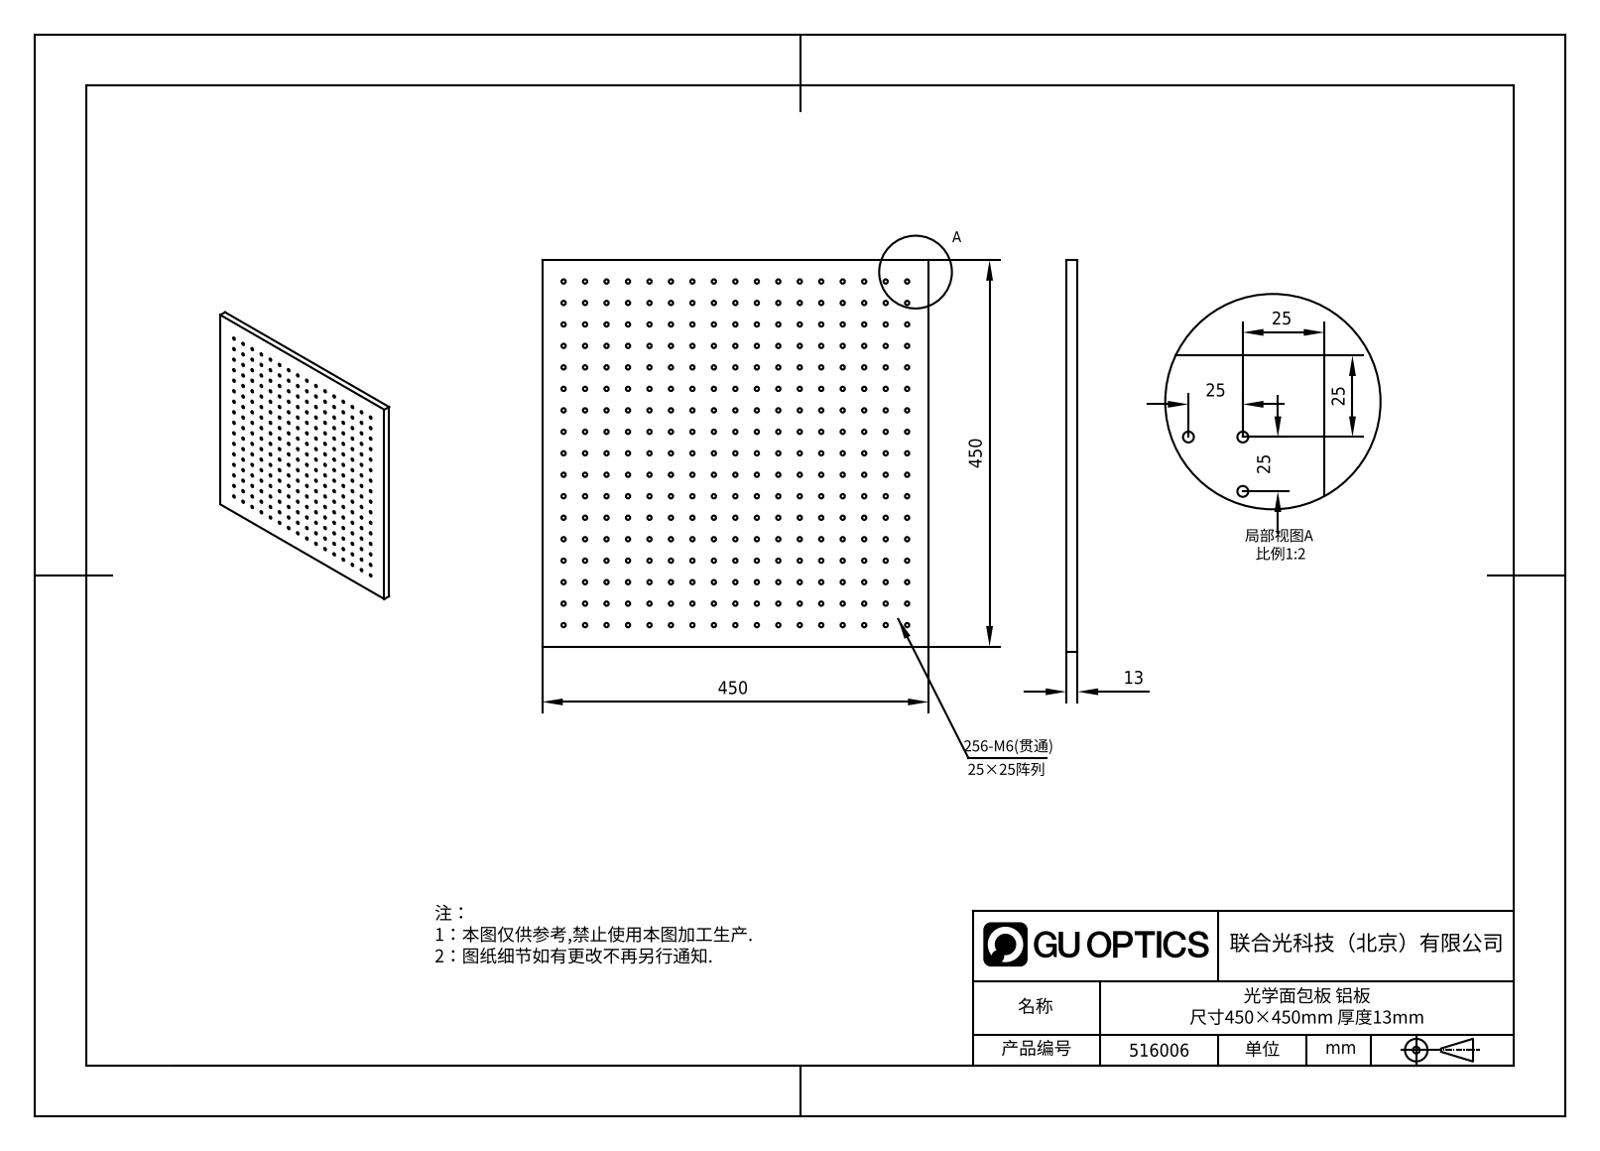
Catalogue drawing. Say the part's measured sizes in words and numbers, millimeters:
The part is named "516006". Its 3-D file was written by "SolidWorks 2020 (CONFIG_CONTROL_DESIGN)". It is 1 solid with 584 faces: 6 planar, 578 cylindrical and 0 other. Overall it measures 450 by 450 by 13 millimeters. Its volume is 2 559 000 cubic millimeters and its surface area 476 066 square millimeters. Round holes: 289 of diameter 5. The main face-to-face distances are 13, 450. The hole center spacings are 25, 50, 75, 100, 125, 150, 175, 200.
